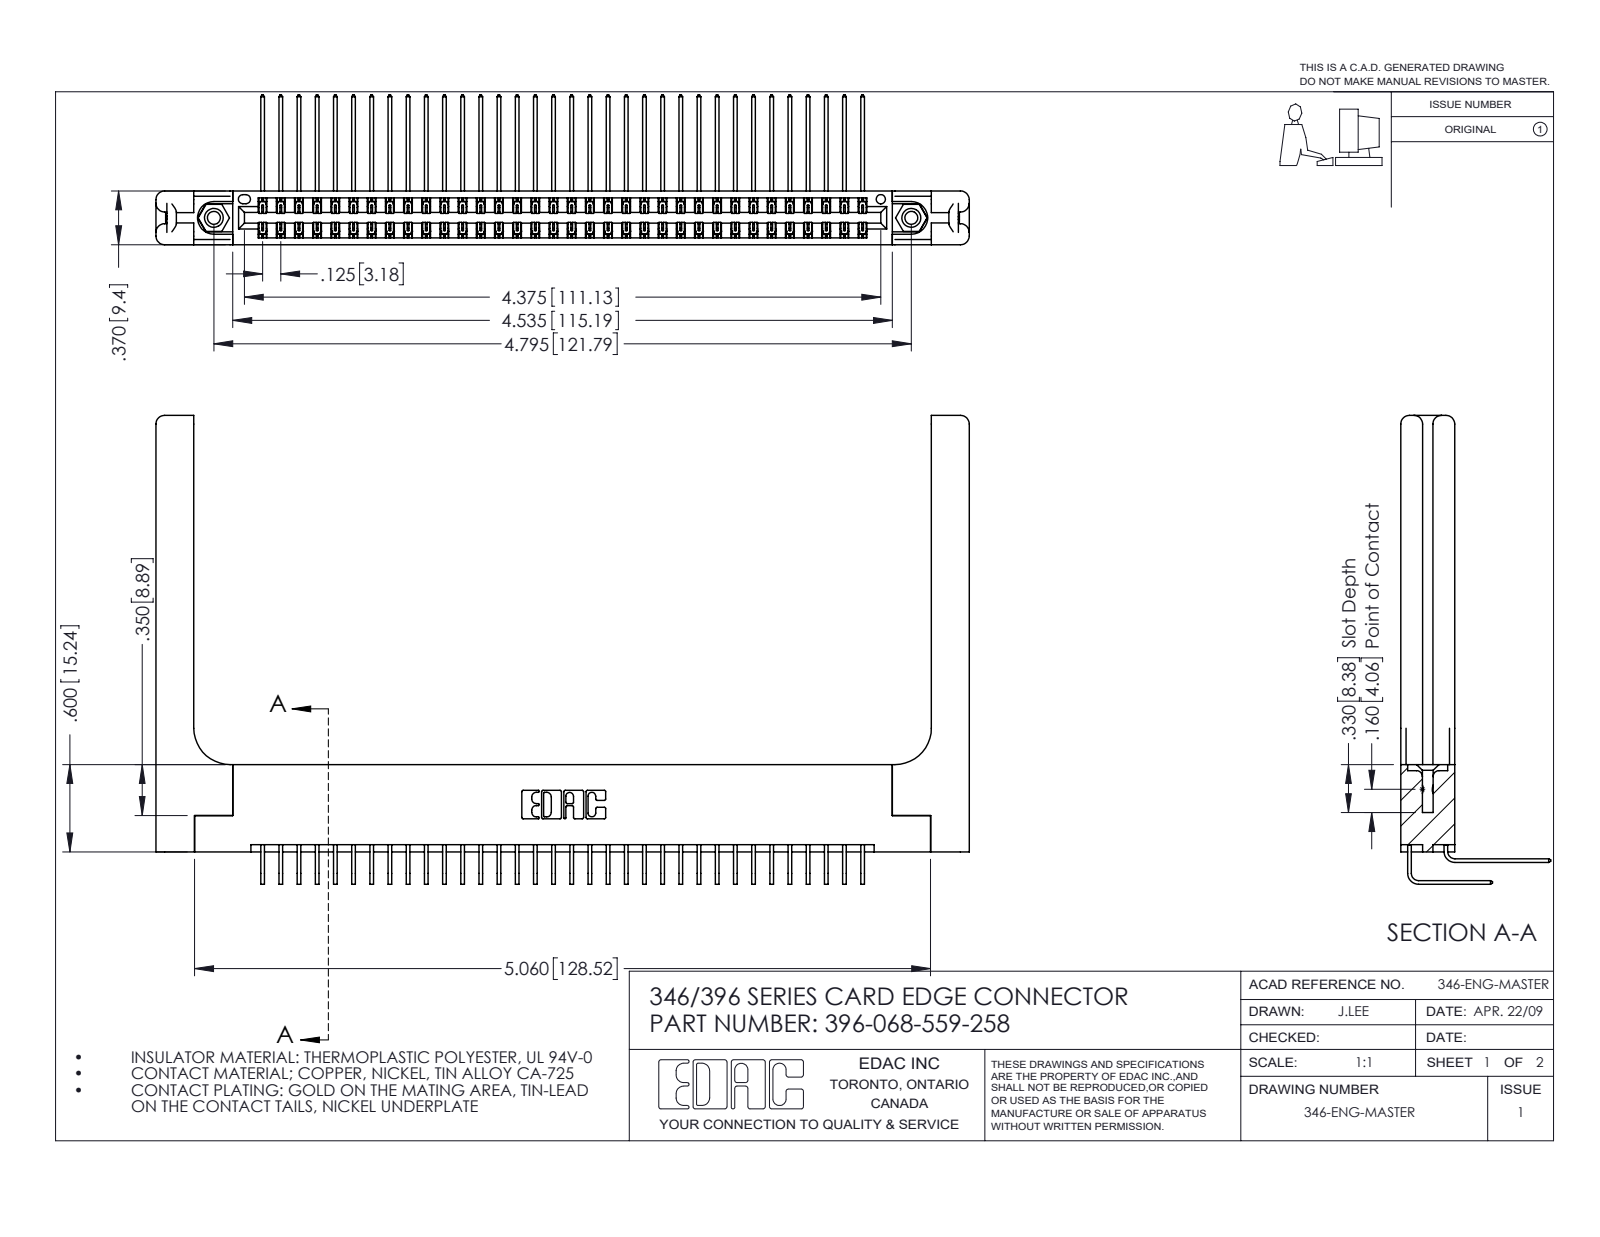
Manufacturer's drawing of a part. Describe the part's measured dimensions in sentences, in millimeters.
The part is named "346-220-058_345-220-058; 345-292-001_559 Tail - 2; 346 Part_Flush Mounting Lugs - 0.156 Dia-TH; 396-068-559-258 (+2 more)". Its 3-D file was written by "SolidWorks 2016 (CONFIG_CONTROL_DESIGN)". It is 73 solids with 4050 faces: 2740 planar, 1250 cylindrical and 60 other. Overall it measures 142 by 81.9 by 26.2 millimeters. Its volume is 21 680 cubic millimeters and its surface area 26 220 square millimeters. Round holes: 2 of diameter 2.3, 2 of diameter 3.2, 2 of diameter 4, 1 of diameter 1.6. Round bosses or shafts: 2 of diameter 3.9. Partial cylindrical surfaces (rounded edges, fillets, slot ends): 102 of radius 0.2, 22 of radius 0.3, 16 of radius 1.5, 6 of radius 0.2, 6 of radius 0.8, 3 of radius 0.7, 2 of radius 0.4, 2 of radius 0.6. The main face-to-face distances are 1.2, 9.4, 8.2, 1.8, 0.6, 3.8, 3.8, 6.4, 7.6, 7. The hole center spacings are 6.2, 116.5, 121.8.
